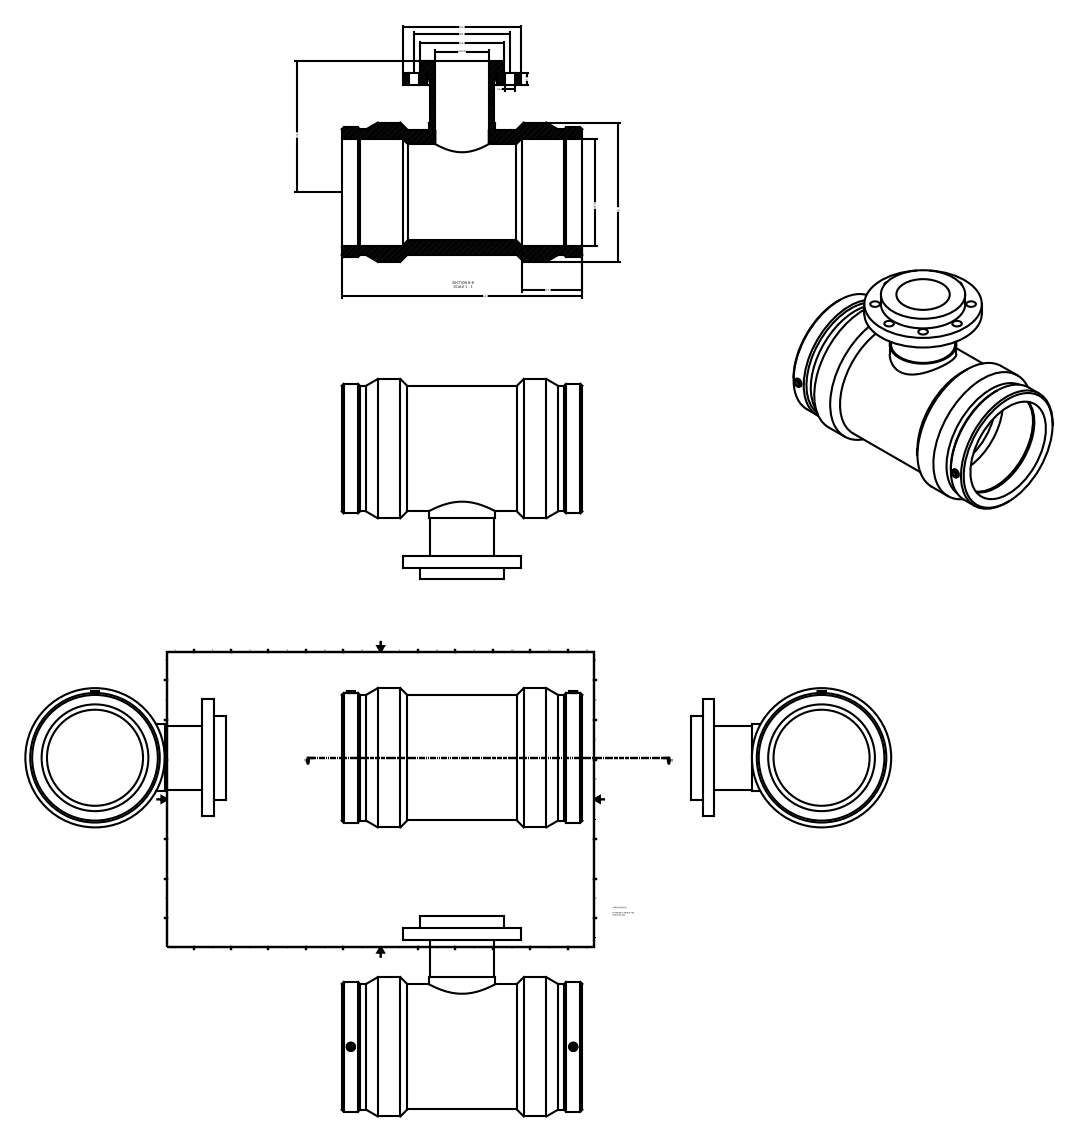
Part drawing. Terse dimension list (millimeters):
name: 499404200100
written by: Autodesk Inventor 2015 (AUTOMOTIVE_DESIGN)
unit: mm
bodies: 1 solid, 60 faces (14 planar, 30 cylindrical, 16 other)
size: 451 × 375.5 × 261
volume: 9 008 000 mm³; area: 835 176 mm²
holes: 8× ⌀18, 2× ⌀10, 1× ⌀100, 1× ⌀130, 1× ⌀180, 1× ⌀200
bosses: 2× ⌀4, 1× ⌀261, 1× ⌀242.73, 1× ⌀235.45, 1× ⌀234.9, 1× ⌀220, 1× ⌀158, 1× ⌀125
face distances: 22, 451, 44, 114.5, 92.5, 70.5, 34.08, 416.92, 382.84, 14
hole spacings: 68.88, 90, 127.28, 166.3, 180, 416.8
